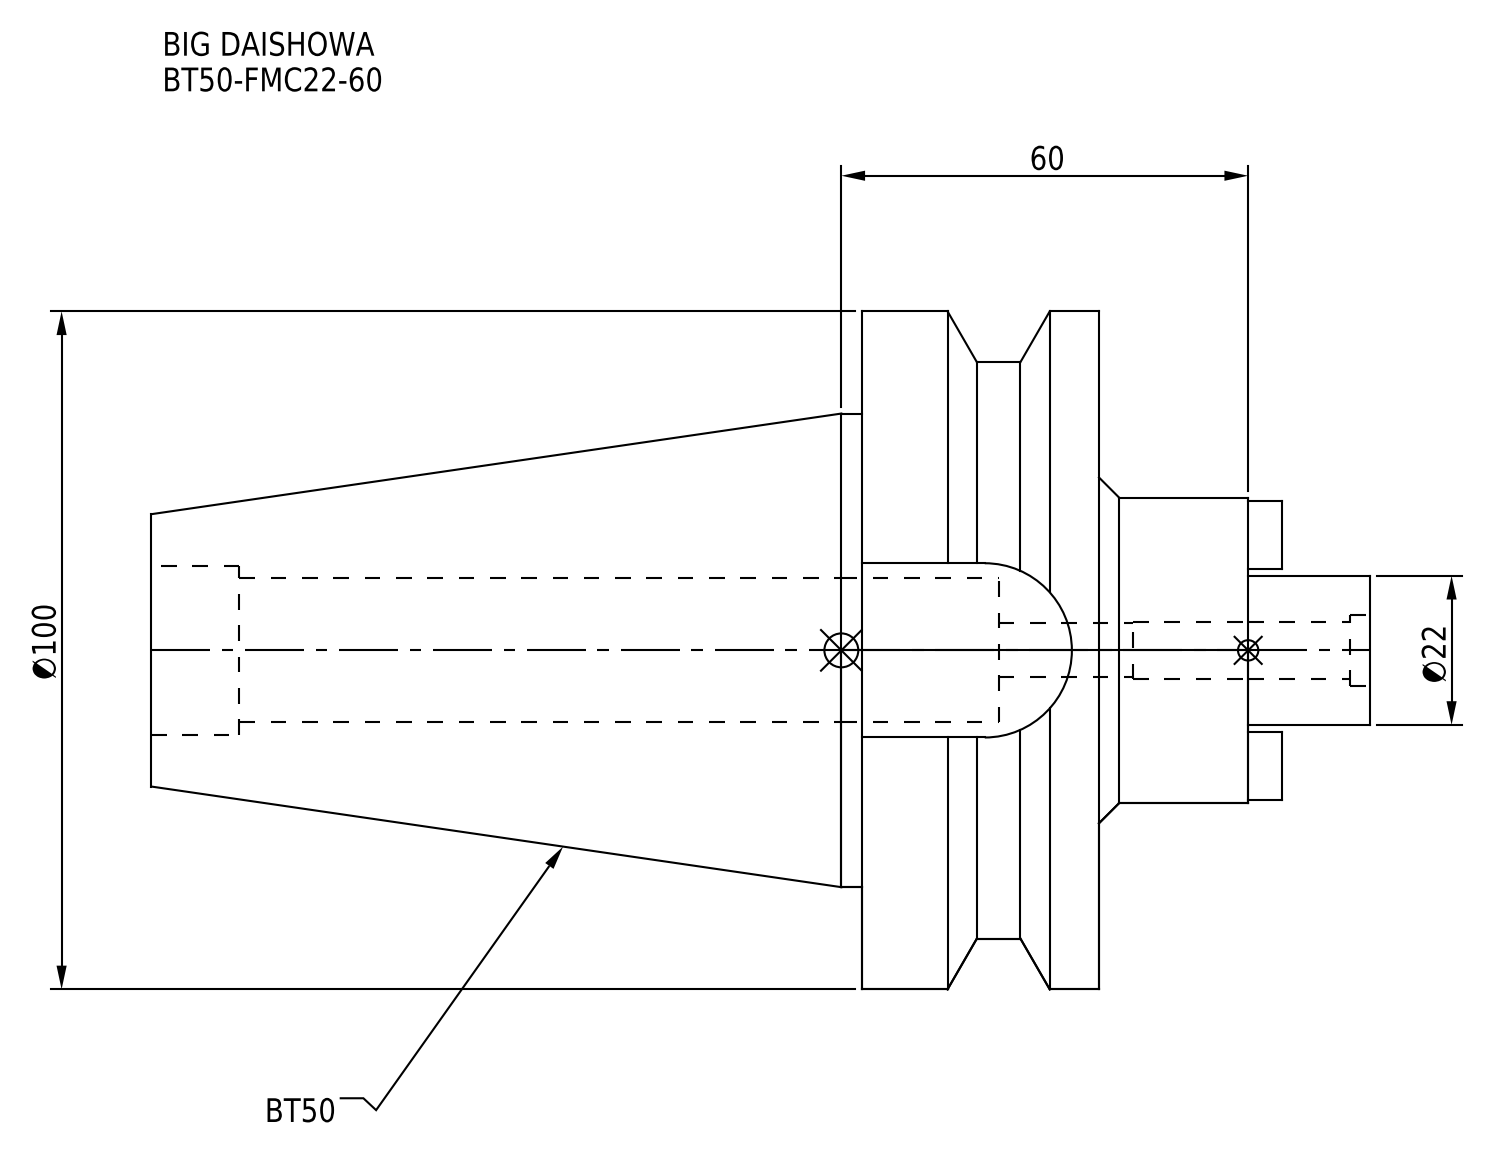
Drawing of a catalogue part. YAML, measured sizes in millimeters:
part_name: "BT50-FMC22-60"
step_written_by: "CREO PARAMETRIC BY PTC INC, 2016380 (AUTOMOTIVE_DESIGN)"
units: millimeters
bodies: {solids: 1, faces: 67, planar: 31, cylindrical: 28, other: 8}
overall_size: [179.8, 100, 100]
volume: 488539
surface_area: 59485
round_holes:
  - {diameter: 8, count: 1}
  - {diameter: 8.5, count: 1}
  - {diameter: 10.5, count: 1}
  - {diameter: 21.2, count: 1}
  - {diameter: 25, count: 1}
round_bosses_or_shafts:
  - {diameter: 100, count: 1}
  - {diameter: 85, count: 1}
  - {diameter: 69.85, count: 1}
  - {diameter: 45, count: 1}
  - {diameter: 22, count: 1}
partial_cylinders:
  - {radius: 12.85, count: 1}
face_to_face_distances: [35, 22, 57, 161.8, 139.8, 104.8, 70.8, 25.7, 13, 166.8]
